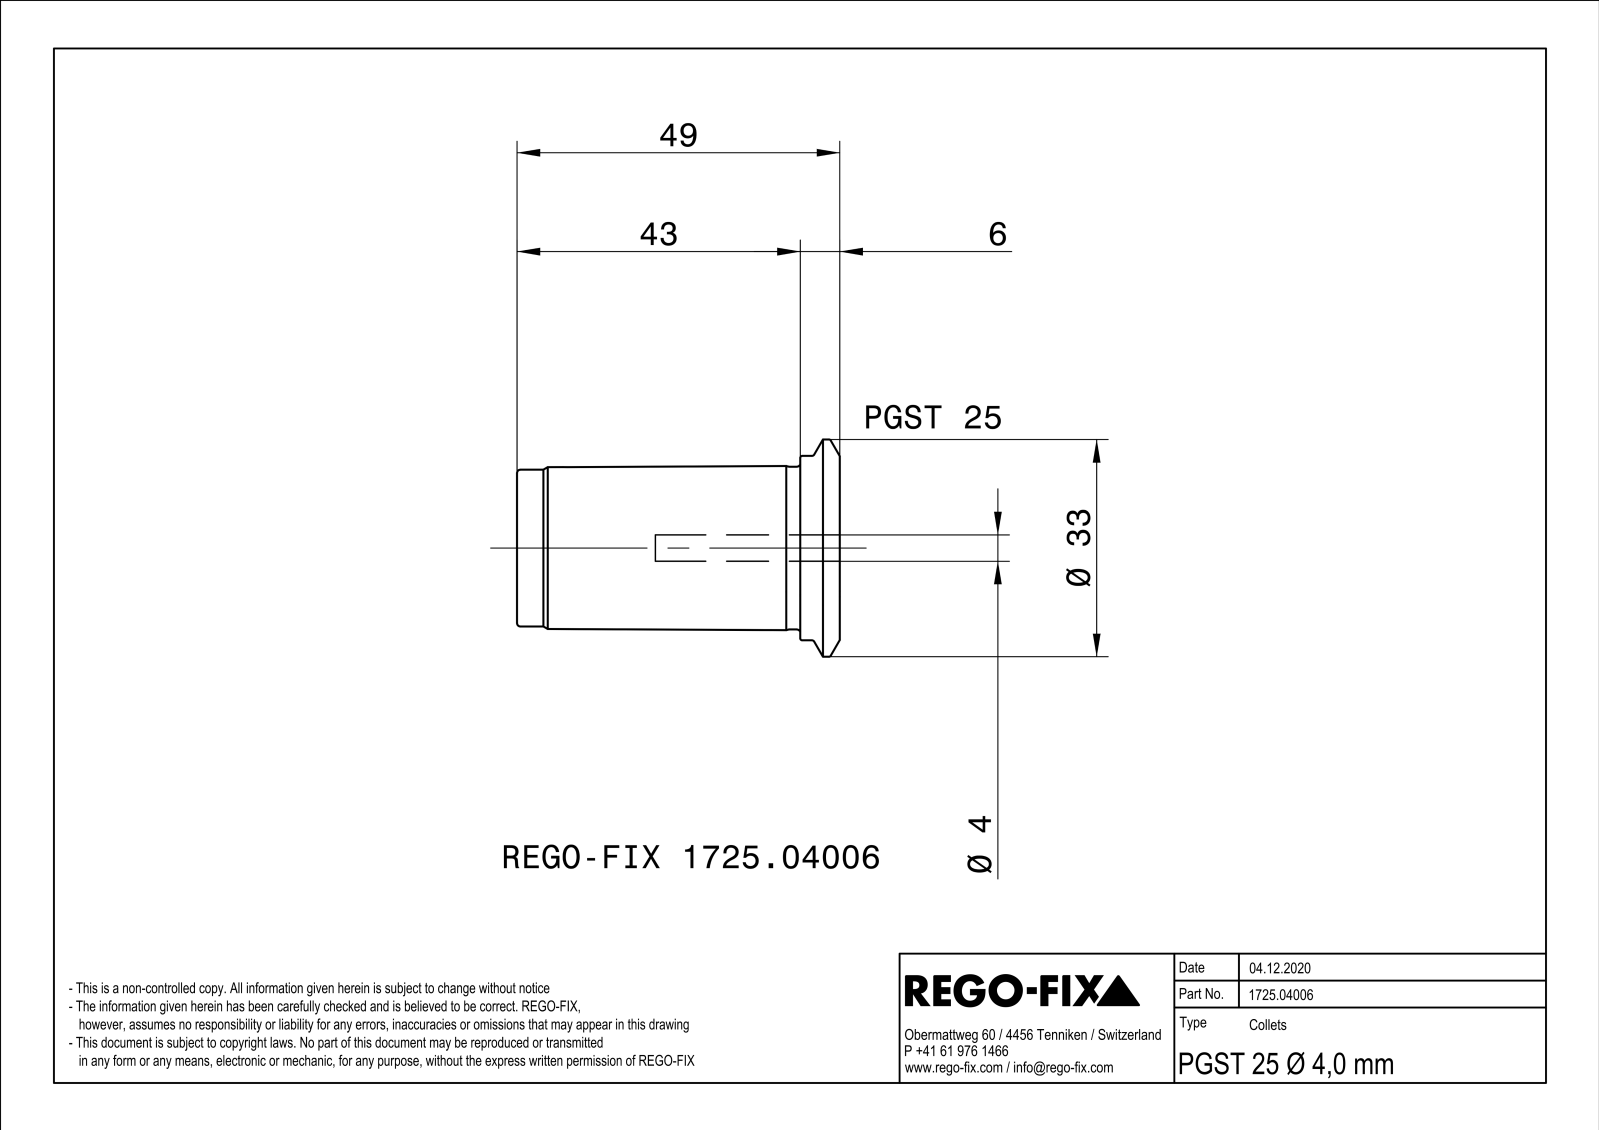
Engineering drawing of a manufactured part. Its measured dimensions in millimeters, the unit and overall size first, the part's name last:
Units: millimetres
Overall size (bounding box): 49 × 32.98 × 32.98
Round holes (diameter × count): ⌀3 ×4, ⌀1.5 ×1, ⌀4 ×1, ⌀5.2 ×1, ⌀17 ×1, ⌀21.19 ×1, ⌀22.3 ×1
Round bosses / shafts (diameter × count): ⌀32.98 ×1, ⌀28 ×1, ⌀24.7 ×1, ⌀23.8 ×1, ⌀22 ×1, ⌀21 ×1, ⌀5 ×1, ⌀2.8 ×1
Main face-to-face distances: 43.5, 49, 5.5, 6, 37.5, 43, 28, 22, 15.5, 21
Hole centre spacings: 6.5, 11.26
Volume: 23 278 mm³ · Surface area: 7 945 mm²
Bodies: 2 solids, 56 faces (14 planar, 18 cylindrical, 24 other)
Part name (STEP PRODUCT): NOCUT
STEP written by: SIEMENS PLM Software Solid Edge ST10 (AUTOMOTIVE_DESIGN)
